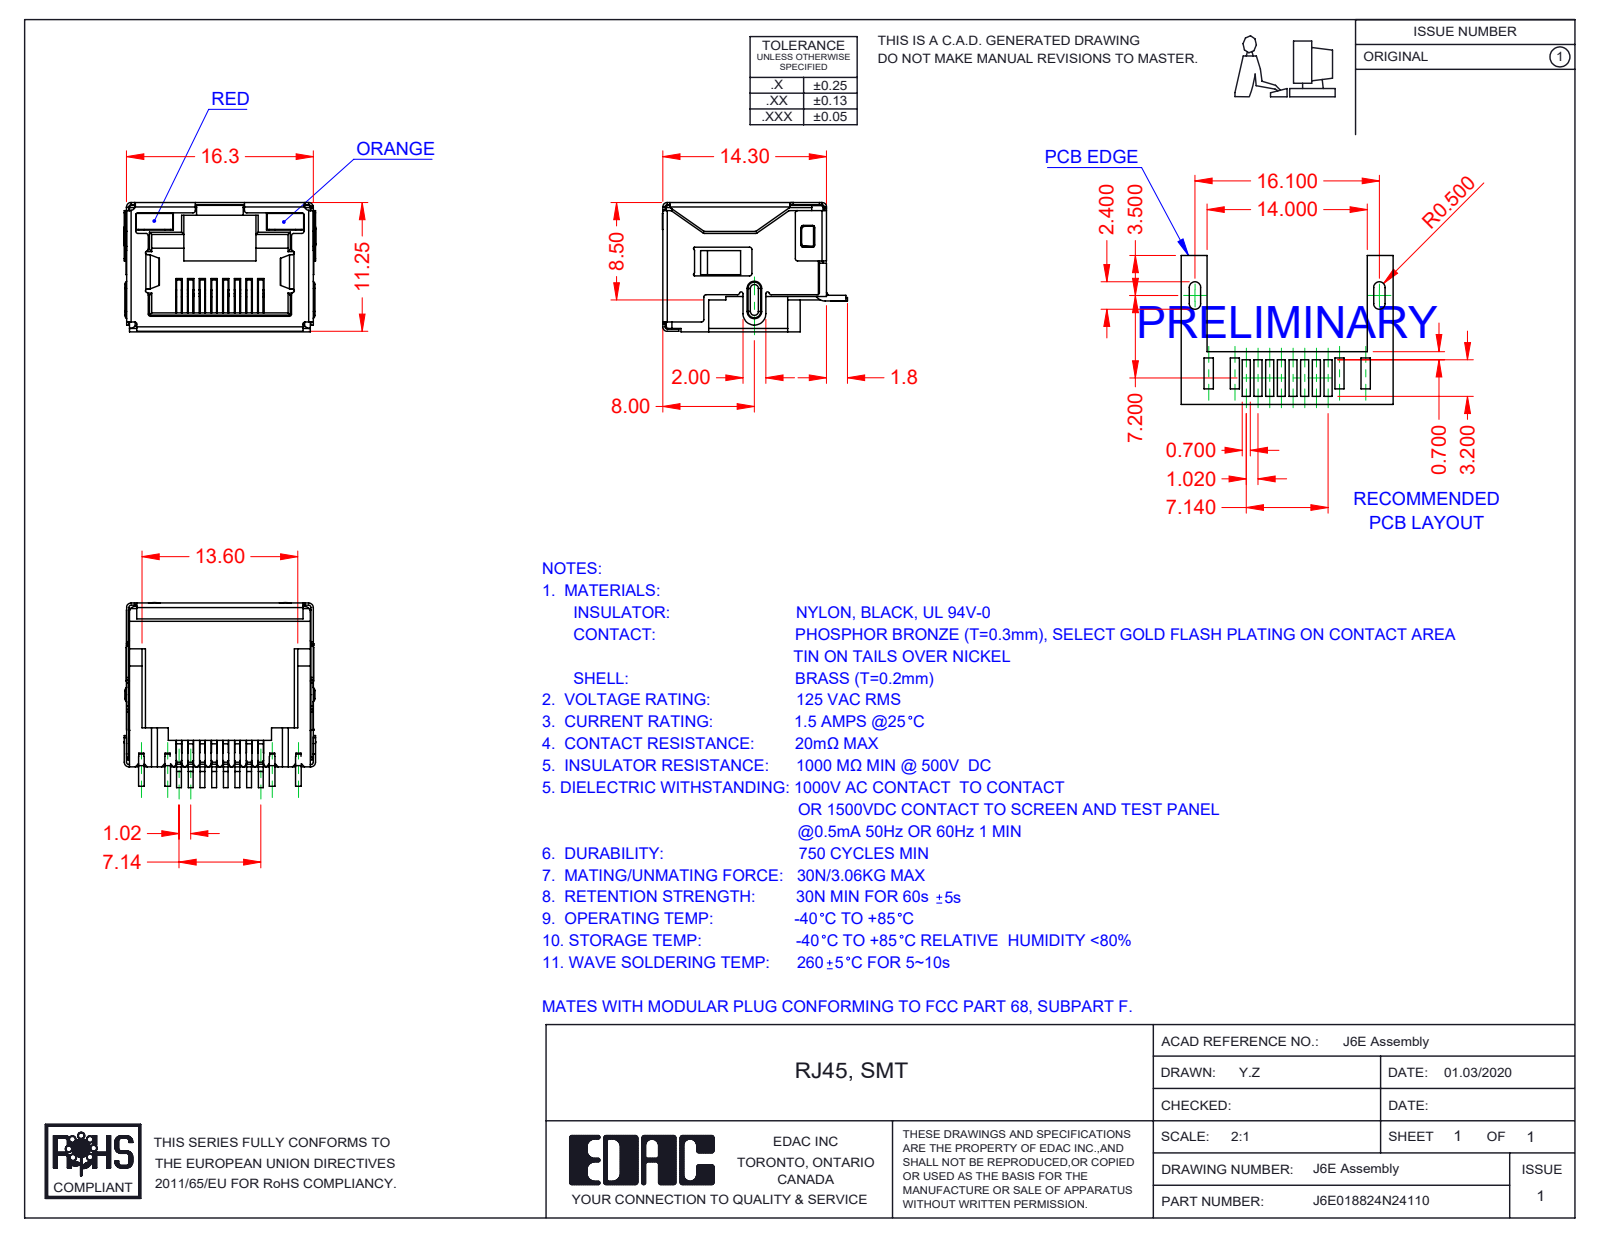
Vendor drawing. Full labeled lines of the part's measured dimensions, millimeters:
Part name (STEP PRODUCT): 6E Insulator_LED; 6E Contacts; J6E018824N24110; 6E LED RH_4-Orange (+2 more)
STEP written by: SolidWorks 2016 (CONFIG_CONTROL_DESIGN)
Units: millimetres
Bodies: 12 solids, 1496 faces (1099 planar, 347 cylindrical, 50 other)
Overall size (bounding box): 16.75 × 16.15 × 11.3
Volume: 1 109 mm³ · Surface area: 4 045 mm²
Partial cylindrical surfaces — rounded edges, fillets, slot ends (radius × count): R0.2 ×82, R0.25 ×17, R0.4 ×13, R0.5 ×13, R0.1 ×10, R0.15 ×7, R0.3 ×4, R1 ×3
Main face-to-face distances: 11.05, 16.05, 16.1, 15.85, 11.1, 11.3, 2.4, 0.7, 9.85, 0.49
